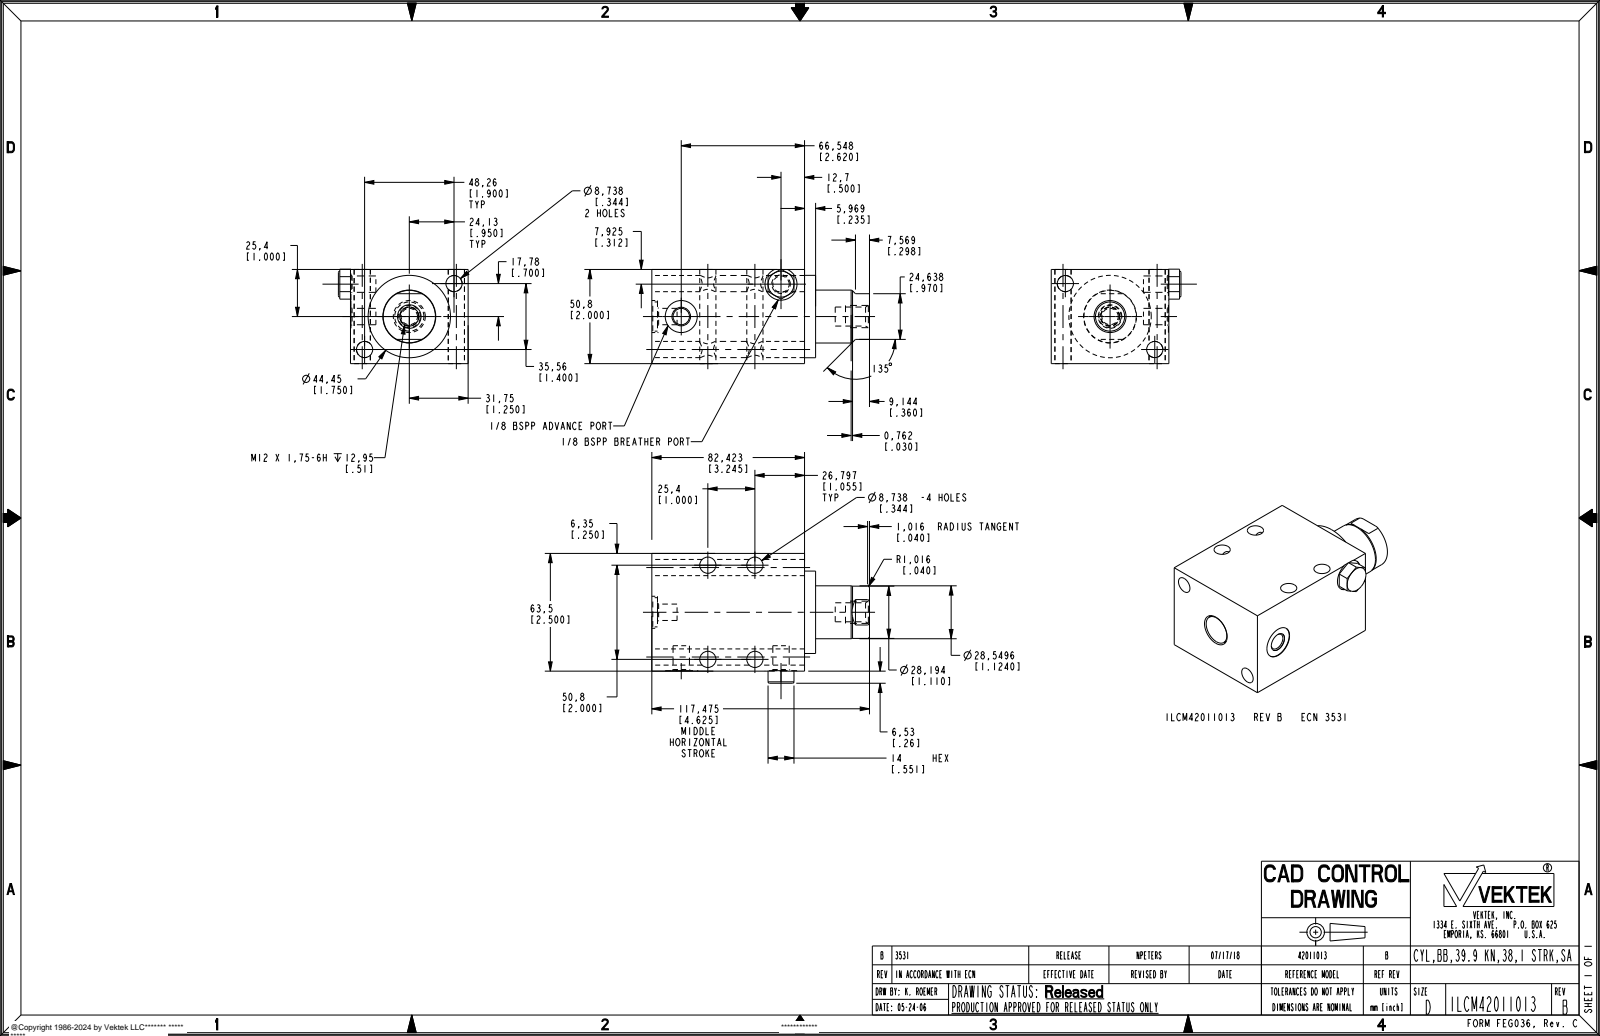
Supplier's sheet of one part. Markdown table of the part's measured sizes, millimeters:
| quantity | value |
| --- | --- |
| part name | ILCM42011013 |
| STEP written by | PRO/ENGINEER BY PARAMETRIC TECHNOLOGY CORPORATION, 2013320 (AUTOMOTIVE_DESIGN) |
| units | millimeters |
| bodies | 1 solid, 100 faces (37 planar, 49 cylindrical, 14 other) |
| overall size | 117.47 × 70.03 × 50.94 |
| volume | 269 774 mm³ |
| surface area | 39 888 mm² |
| round holes (diameter × count) | 8.74 × 6, 8.84 × 3, 10.03 × 3, 17.27 × 3, 10.26 × 1 |
| round bosses / shafts (diameter × count) | 44.45 × 1, 28.55 × 1, 28.19 × 1, 15.75 × 1, 12 × 1 |
| main face-to-face distances | 50.8, 63.5, 82.42, 5.97, 88.39, 29.08, 35.05, 117.47, 63.25, 13.08 |
| hole center spacings | 25.4, 29.97, 50.8, 56.8, 56.62, 59.95 |
